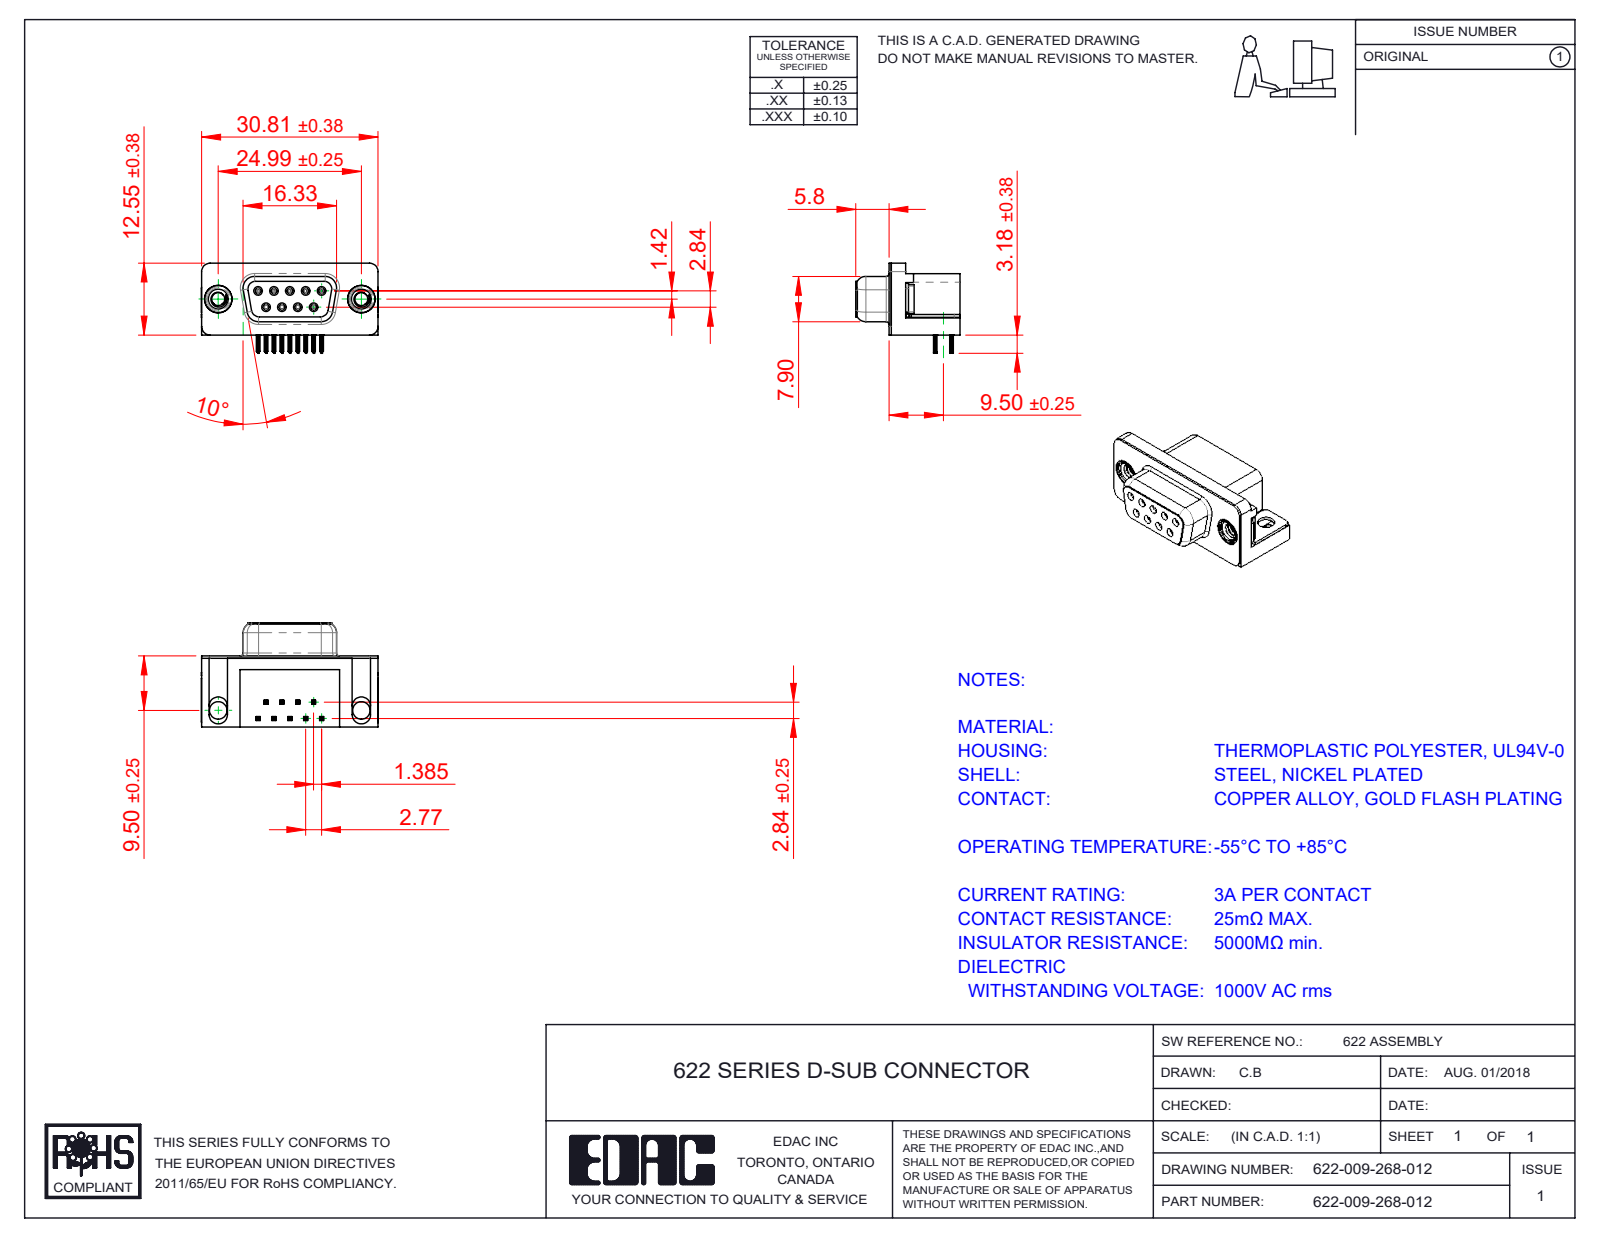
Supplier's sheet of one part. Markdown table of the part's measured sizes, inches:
| quantity | value |
| --- | --- |
| part name | 622 4-40 Threaded Rivet; 622-009-268-012; 622 Thru Hole Board Mount; 622 Contact Top (+3 more) |
| STEP written by | SolidWorks 2016 (CONFIG_CONTROL_DESIGN) |
| units | inches |
| bodies | 15 solids, 1570 faces (682 planar, 416 cylindrical, 472 other) |
| overall size | 1.216 × 0.717 × 0.619 |
| volume | 0.227 in³ |
| surface area | 7.845 in² |
| round holes (diameter × count) | 0.031 × 9, 0.035 × 9, 0.089 × 2, 0.12 × 2, 0.157 × 2, 0.189 × 2, 0.197 × 2 |
| round bosses / shafts (diameter × count) | 0.047 × 9, 0.193 × 2, 0.187 × 2, 0.154 × 2 |
| partial cylindrical surfaces (radius × count) | 0.004 × 72, 0.006 × 36, 0.014 × 18, 0.039 × 18, 0.013 × 9, 0.01 × 8, 0.053 × 8, 0.063 × 8 |
| main face-to-face distances | 0.016, 0.472, 0.488, 0.014, 0.114, 0.098, 0.244, 0.407, 0.02, 0.374 |
| hole center spacings | 0.124, 0.109, 0.218, 0.198, 0.198, 0.327, 0.294, 0.295 |
